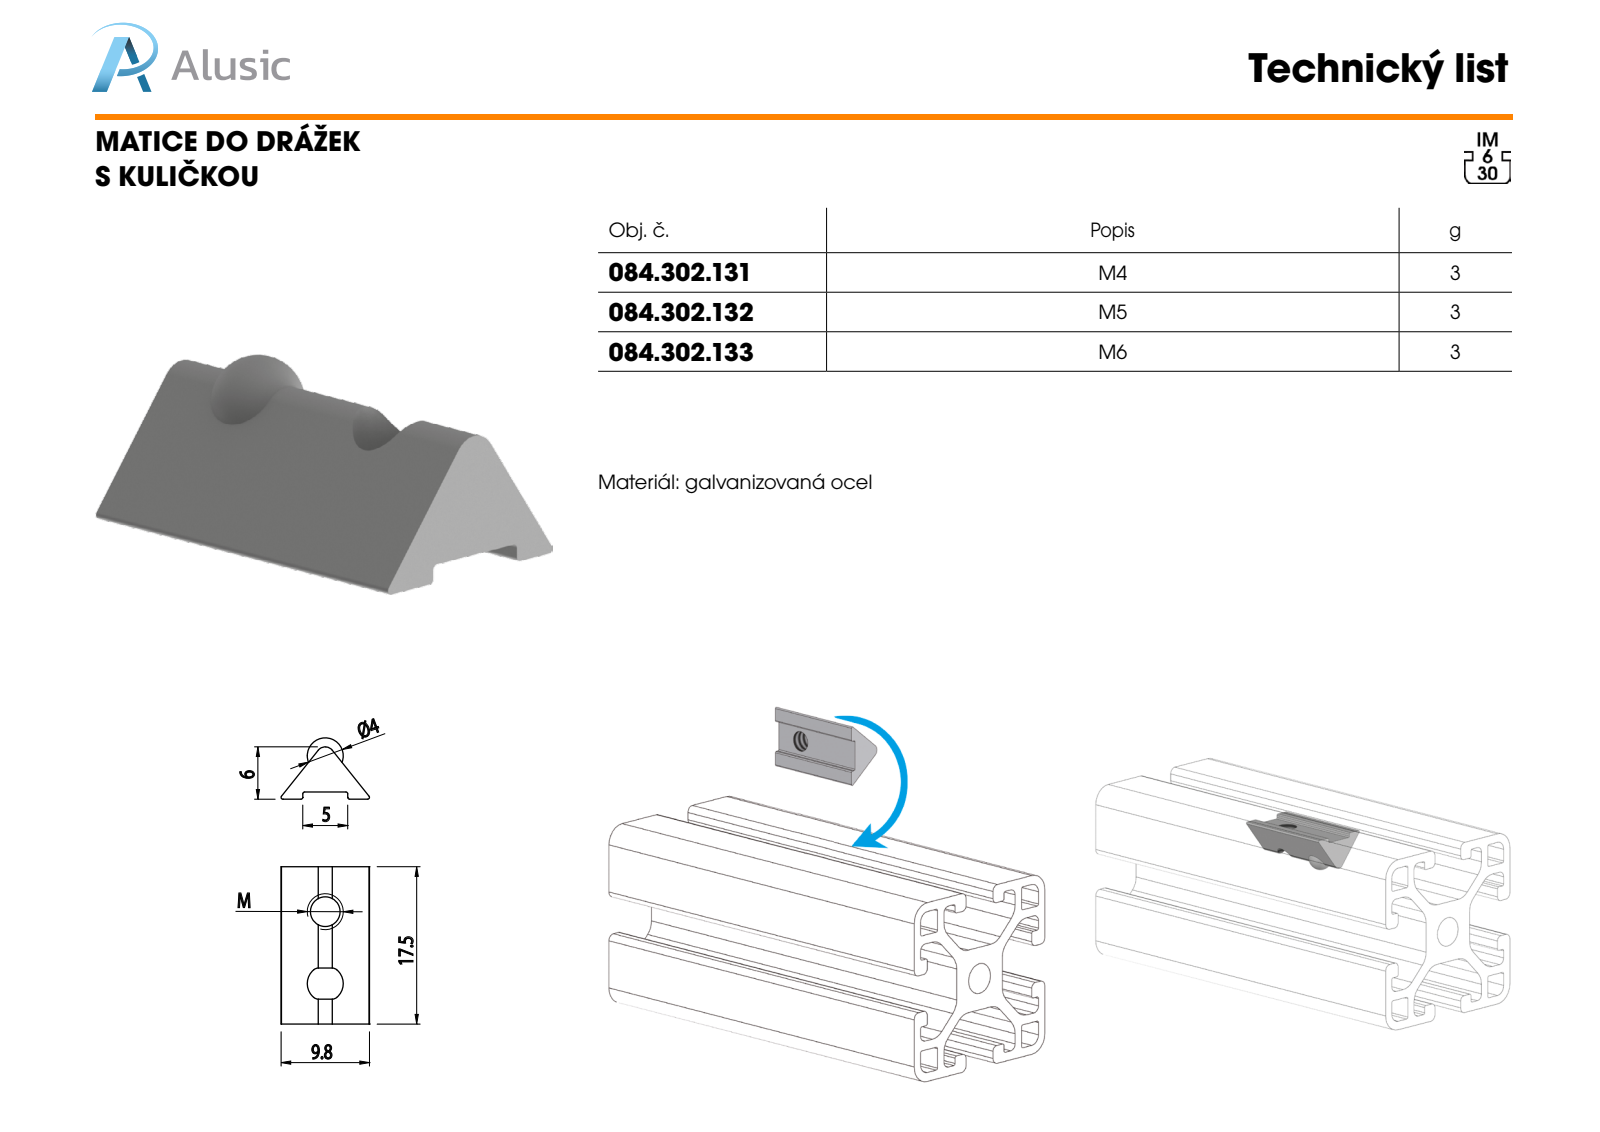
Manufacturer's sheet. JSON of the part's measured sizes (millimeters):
{"part_name": "084.302.132; Dado a culla; Sfera", "step_written_by": "SolidWorks 2016 (CONFIG_CONTROL_DESIGN)", "units": "millimeters", "bodies": {"solids": 2, "faces": 15, "planar": 9, "cylindrical": 4, "other": 2}, "overall_size": [17.5, 9.8, 7.3], "volume_mm3": 567, "surface_area_mm2": 625, "round_holes": [[4.2, 1]], "partial_cylinders_radius": [[3, 2]], "face_to_face_distances": [0.5, 17.5, 5]}
